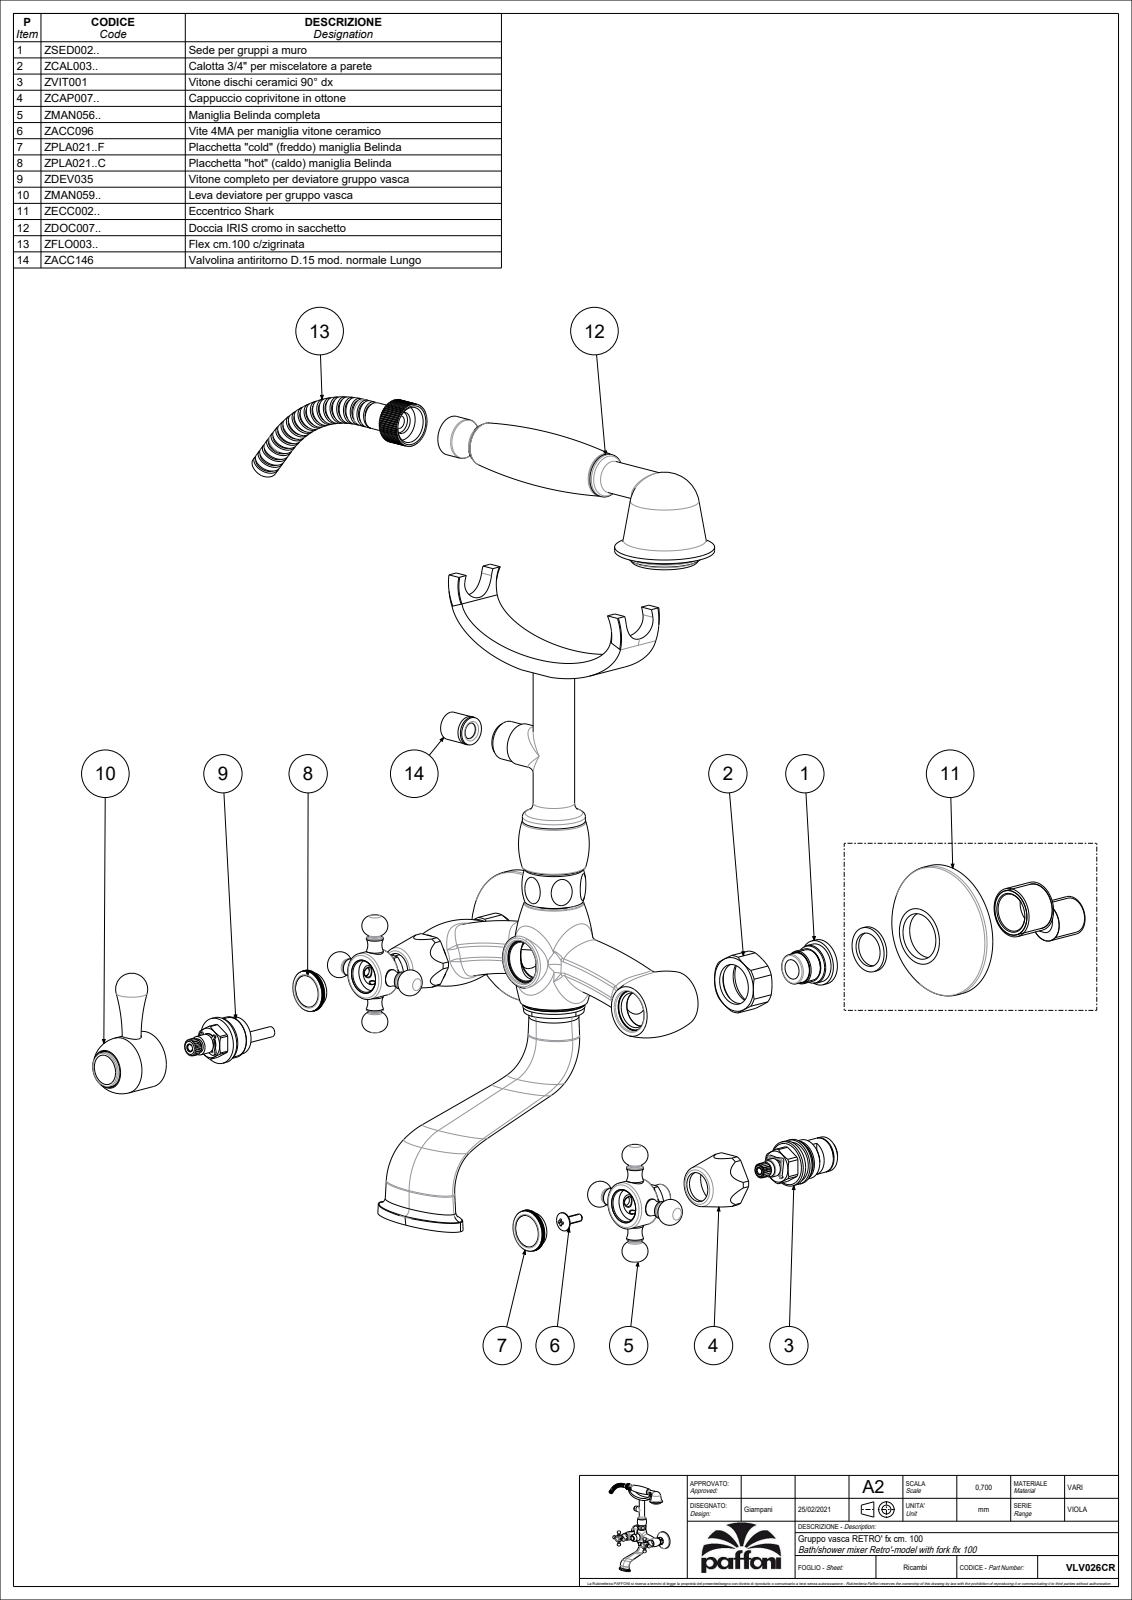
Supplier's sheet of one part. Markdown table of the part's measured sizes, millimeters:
| quantity | value |
| --- | --- |
| part name | VLV026CR |
| STEP written by | CREO PARAMETRIC BY PTC INC, 2020044 (CONFIG_CONTROL_DESIGN) |
| units | millimeters |
| bodies | 6 solids, 1695 faces (680 planar, 446 cylindrical, 569 other) |
| overall size | 337.51 × 297.8 × 165.62 |
| volume | 597 159 mm³ |
| surface area | 176 022 mm² |
| round holes (diameter × count) | 21.5 × 3, 23 × 3, 24.1 × 3, 15.7 × 2, 16.7 × 2, 18.63 × 2, 19 × 2, 26.7 × 2, 14 × 1, 15 × 1, 15.5 × 1, 21 × 1 |
| round bosses / shafts (diameter × count) | 25 × 3, 9 × 3, 7 × 3, 70 × 2, 22 × 2, 20.5 × 2, 14 × 2, 13 × 2 |
| partial cylindrical surfaces (radius × count) | 3.5 × 2, 11 × 2, 14.5 × 2, 15.5 × 2, 5.25 × 1, 10 × 1, 14 × 1 |
| main face-to-face distances | 44, 35.5, 20, 15.5, 23.25, 3.25, 26.5, 8.5, 24, 31.75 |
| hole center spacings | 76.3, 150 |
